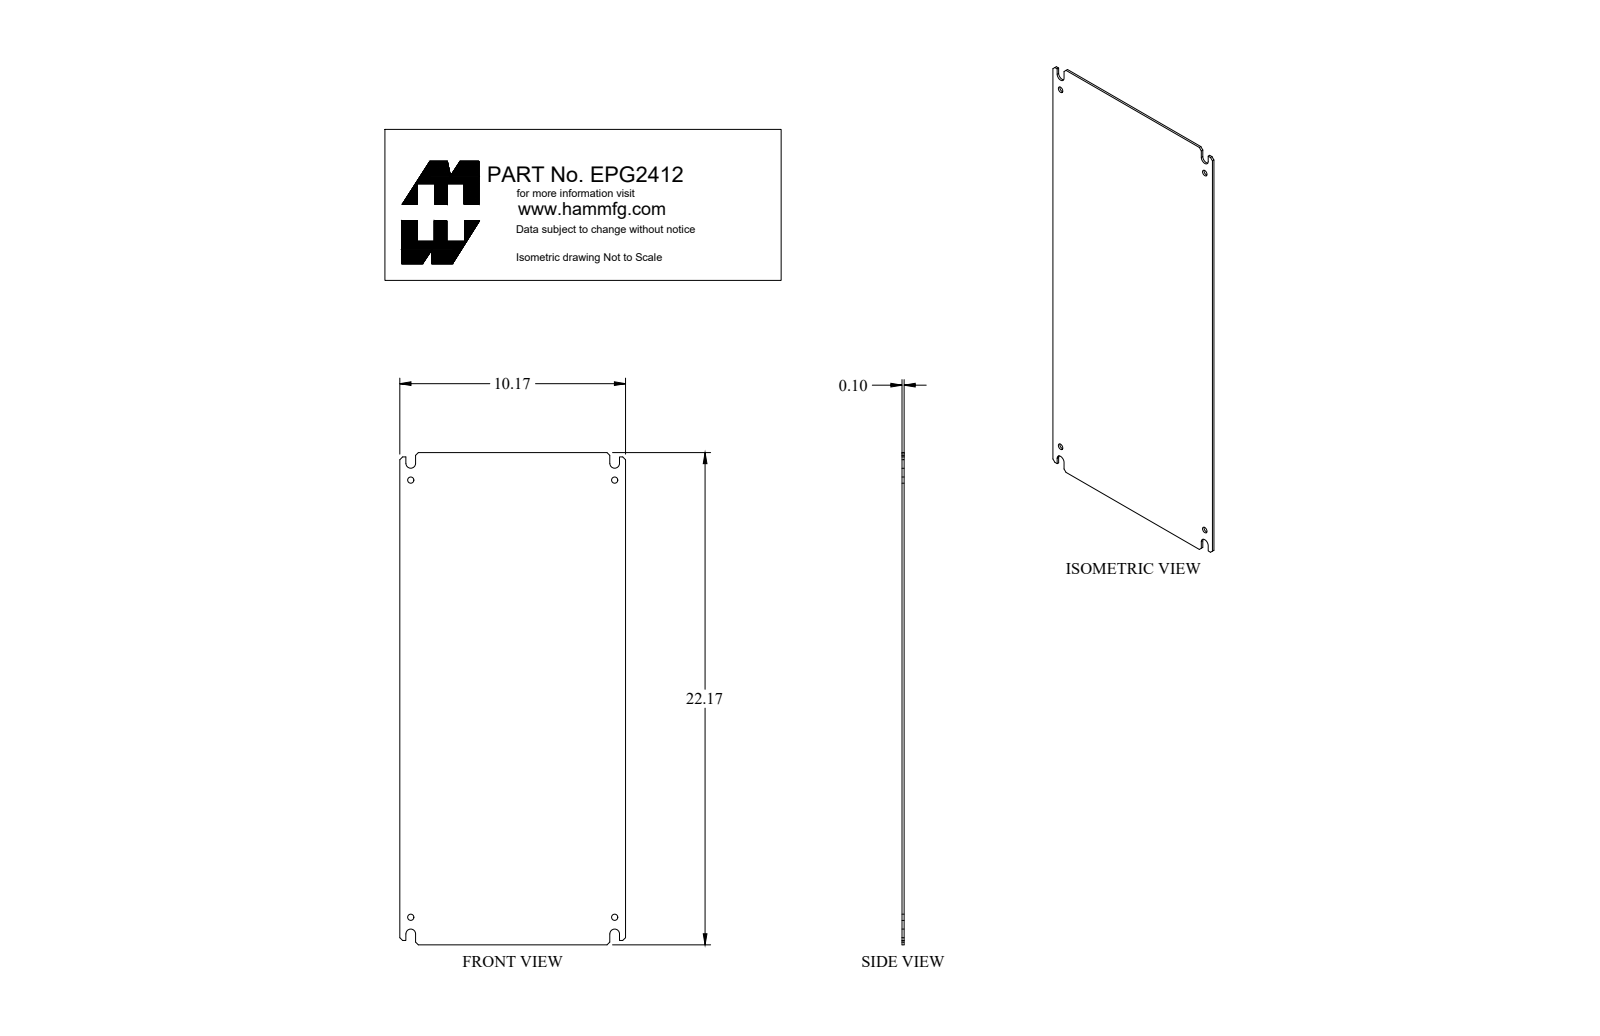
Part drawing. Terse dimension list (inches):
name: EPG2412
written by: SolidWorks 2018 (AUTOMOTIVE_DESIGN)
unit: in
bodies: 1 solid, 40 faces (26 planar, 14 cylindrical, 0 other)
size: 22.17 × 10.17 × 0.095
volume: 21.26 in³; area: 454.3 in²
holes: 4× ⌀0.281
rounds: 4× R0.219
face distances: 0.095, 10.17, 22.17, 0.709, 9.461, 0.272, 9.898, 0.437, 9.188, 8.751
hole spacings: 9.188, 19.688, 21.727
